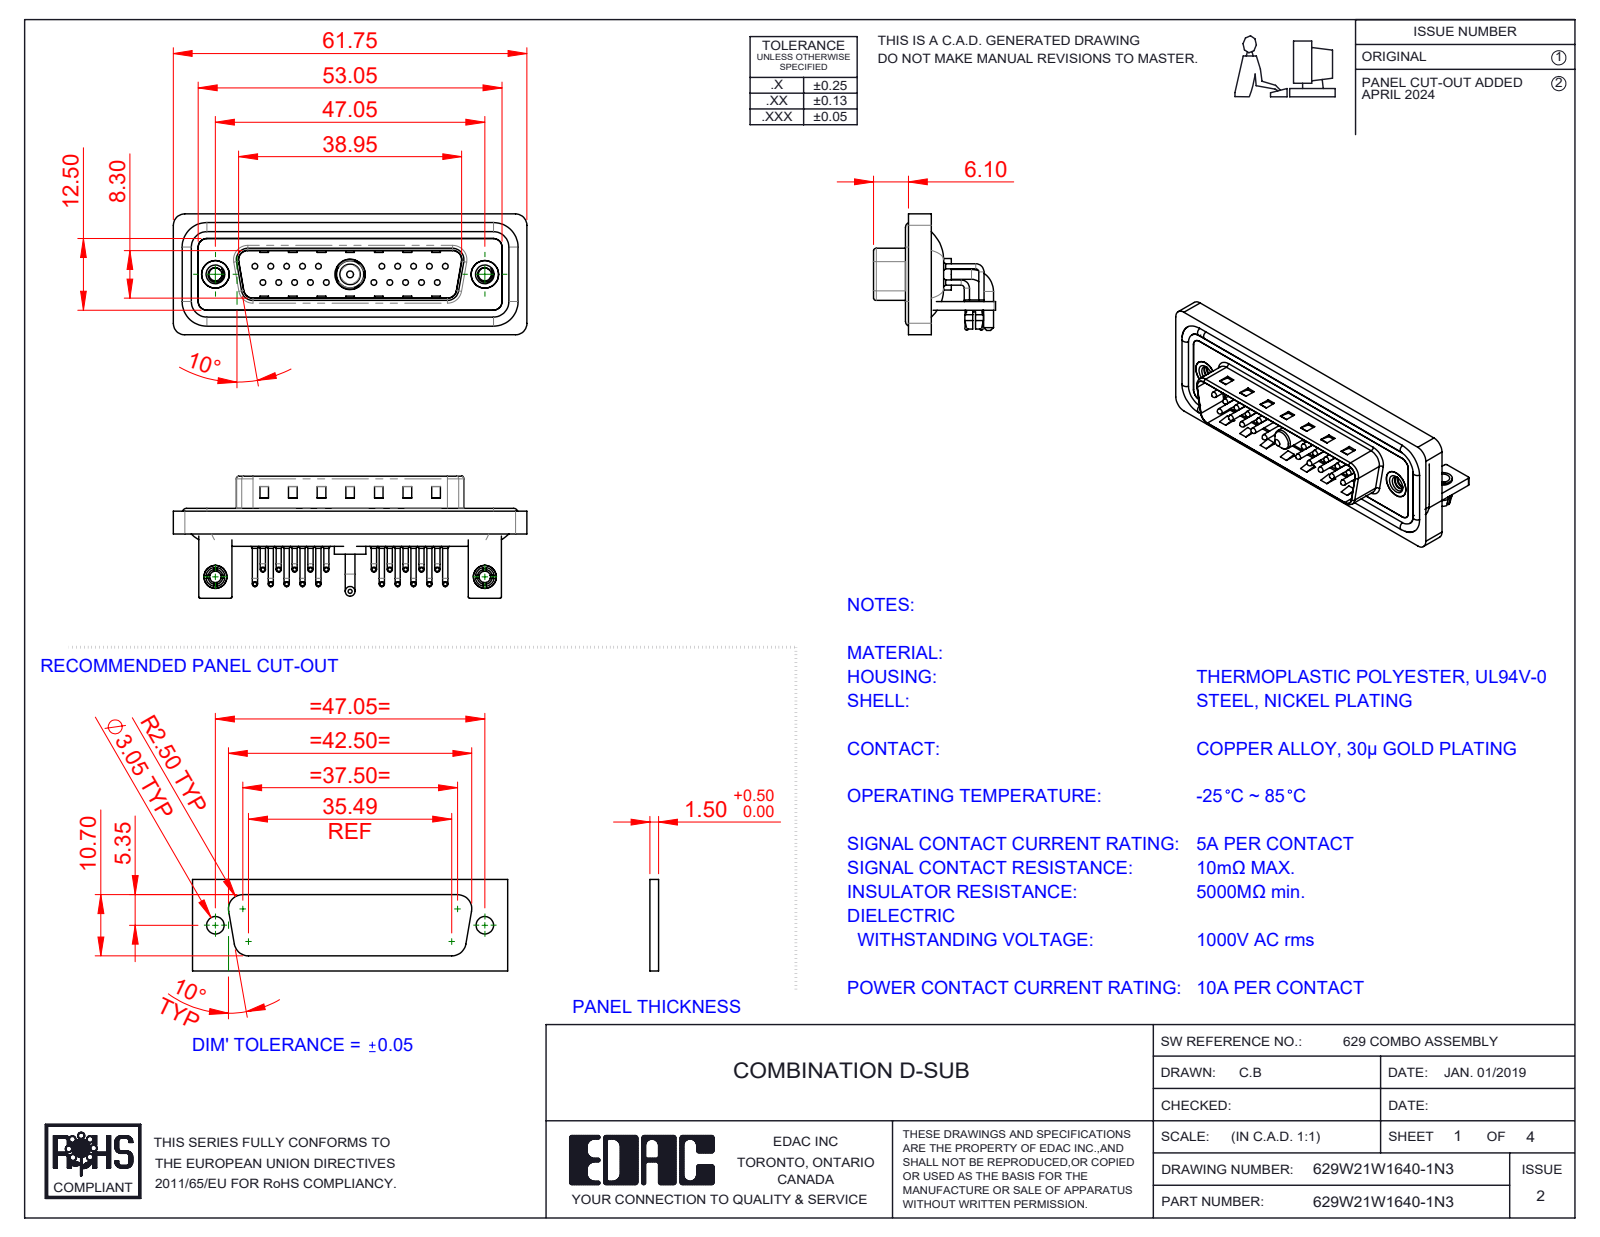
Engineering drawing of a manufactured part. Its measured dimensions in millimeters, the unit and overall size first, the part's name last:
Units: millimetres
Overall size (bounding box): 61.75 × 21.3 × 21.1
Round holes (diameter × count): ⌀2 ×22, ⌀0.75 ×20, ⌀1.6 ×20, ⌀2.26 ×2, ⌀2.5 ×2, ⌀3.2 ×2, ⌀4 ×2, ⌀4.8 ×2, ⌀5 ×2, ⌀4.85 ×1, ⌀5.3 ×1
Round bosses / shafts (diameter × count): ⌀0.9 ×40, ⌀1.5 ×20, ⌀1 ×20, ⌀0.65 ×20, ⌀1.6 ×4, ⌀4.9 ×2, ⌀4 ×2, ⌀3.4 ×2
Partial cylindrical surfaces — rounded edges, fillets, slot ends (radius × count): R1.01 ×20, R2 ×19, R1.5 ×18, R0.25 ×16, R0.5 ×9, R1.6 ×8, R0.6 ×4, R0.65 ×4
Main face-to-face distances: 0.4, 0.8, 2.1, 2.9, 1.5, 1.1, 4.1, 1.6, 4.5, 3.7
Hole centre spacings: 3.16, 2.77, 5.54, 8.31, 5.04, 19.39, 20.97, 22.16
Volume: 7 674 mm³ · Surface area: 13 467 mm²
Bodies: 33 solids, 2858 faces (1567 planar, 979 cylindrical, 312 other)
Part name (STEP PRODUCT): 629Combo Housing_21W1; 629Combo Contact Row 1; 629Combo Shell Front_25 Contacts; 629Combo Shell Rear_25 Contacts (+7 more)
STEP written by: SolidWorks 2023 (CONFIG_CONTROL_DESIGN)
